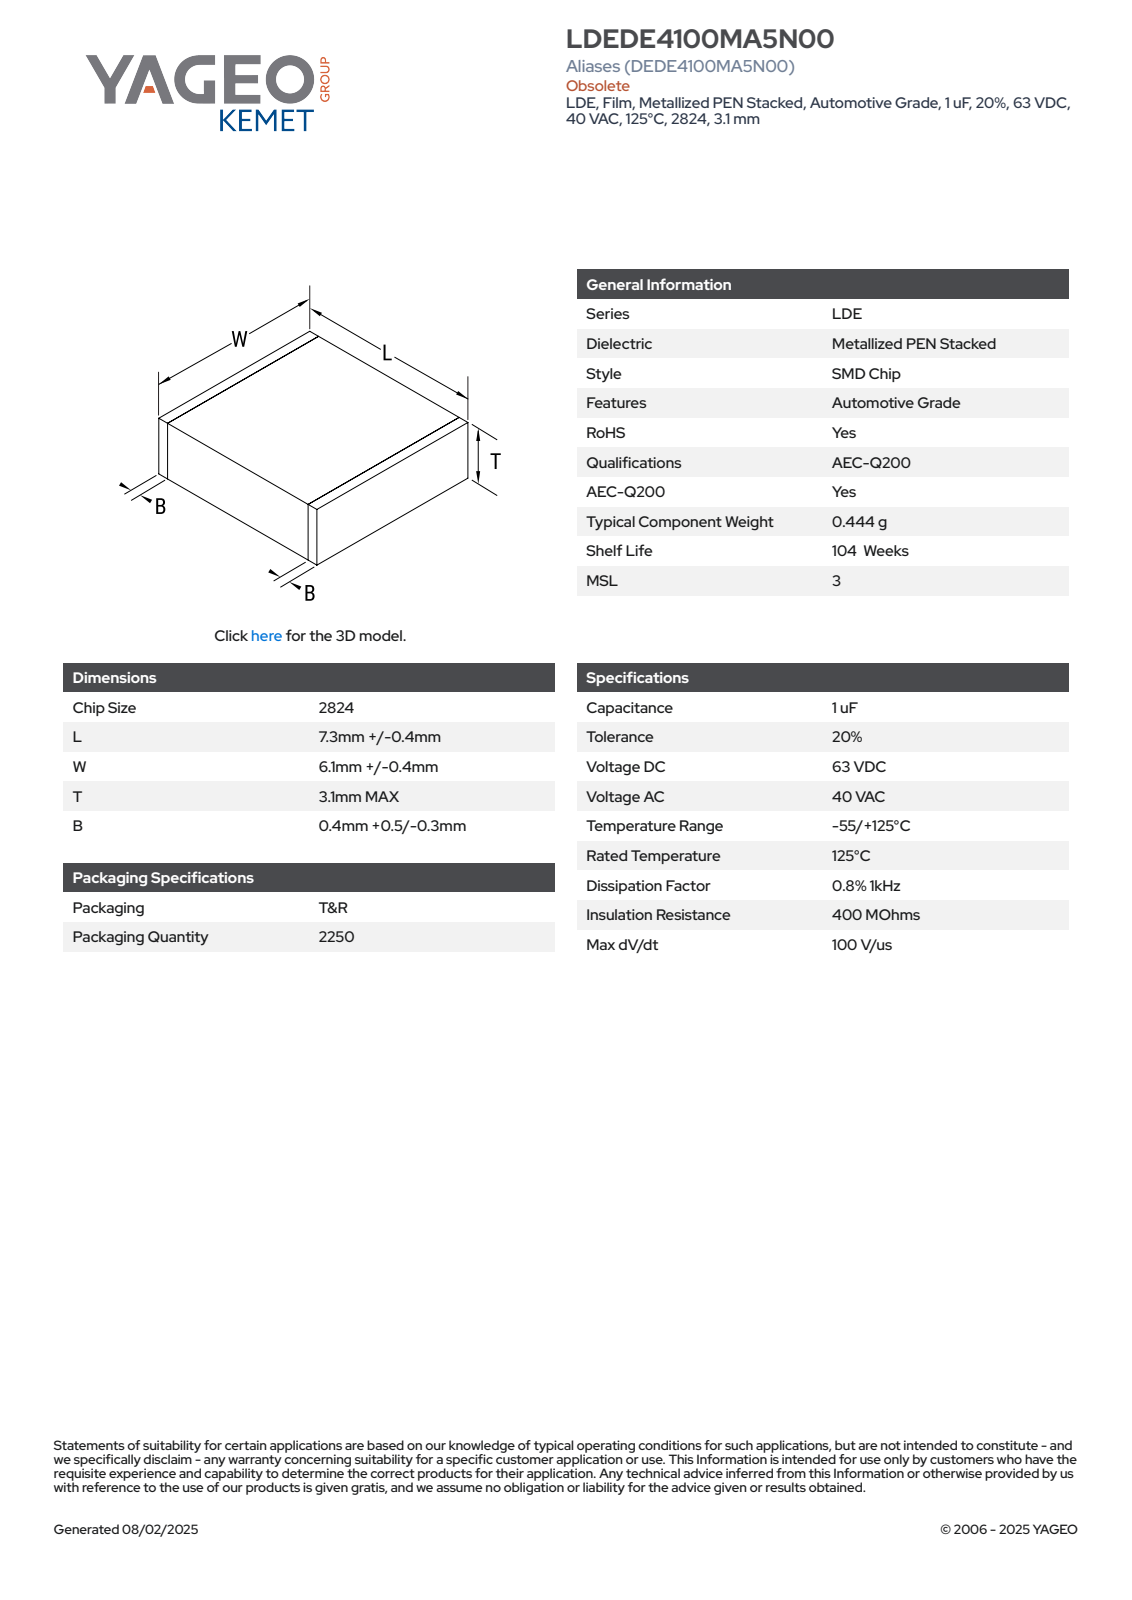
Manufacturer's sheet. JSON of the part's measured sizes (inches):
{"part_name": "CFS_LDELDB_2824_L7.7W6.5T3.1B0.9", "step_written_by": "SolidWorks 2020 (AUTOMOTIVE_DESIGN)", "units": "inches", "bodies": {"solids": 4, "faces": 73, "planar": 73, "cylindrical": 0, "other": 0}, "overall_size": [0.303, 0.256, 0.122], "volume_in3": 0.009, "surface_area_in2": 0.296, "face_to_face_distances": [0.121, 0.255, 0.303, 0.122, 0.122, 0.256, 0.256, 0.02, 0.283, 0.264]}
